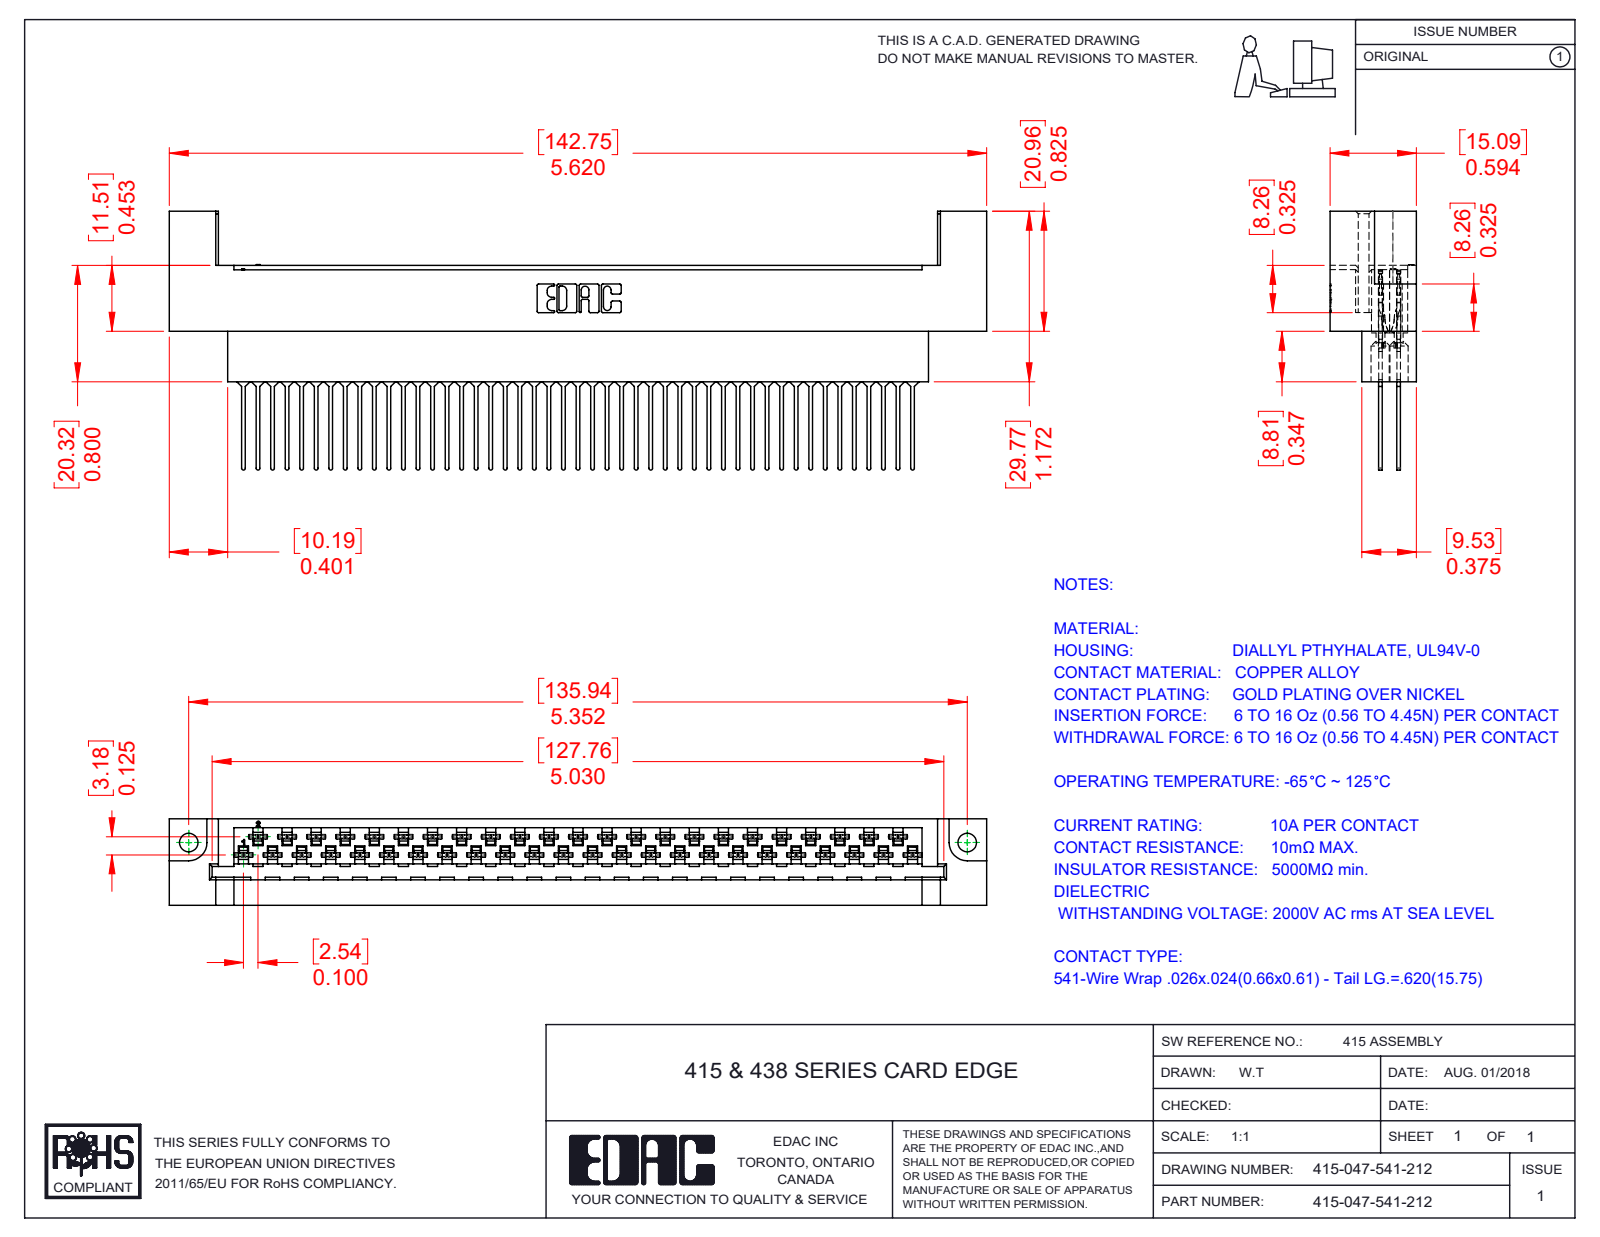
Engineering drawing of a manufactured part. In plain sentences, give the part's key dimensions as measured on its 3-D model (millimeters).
The part is named "415-047-541-212; 516-290-001_541; 415-210-001_415-210-047-212". Its 3-D file was written by "SolidWorks 2016 (CONFIG_CONTROL_DESIGN)". It is 48 solids with 4768 faces: 3055 planar, 1268 cylindrical and 445 other. Overall it measures 142.75 by 45.17 by 15.09 millimeters. Its volume is 27 945 cubic millimeters and its surface area 32 027 square millimeters. Round holes: 47 of diameter 1.27, 47 of diameter 3.3, 2 of diameter 3.25. Partial cylindrical surfaces (rounded edges, fillets, slot ends): 188 of radius 0.3, 188 of radius 0.56, 94 of radius 0.18, 94 of radius 0.2, 94 of radius 0.41, 94 of radius 2.03, 47 of radius 0.33, 22 of radius 0.25. The main face-to-face distances are 3.18, 0.61, 1.88, 15.09, 1.27, 1.94, 0.67, 6.61, 8.48, 6. The hole center spacings are 5.08, 10.16, 15.24, 20.32, 25.4, 30.48, 35.56, 2.54.
